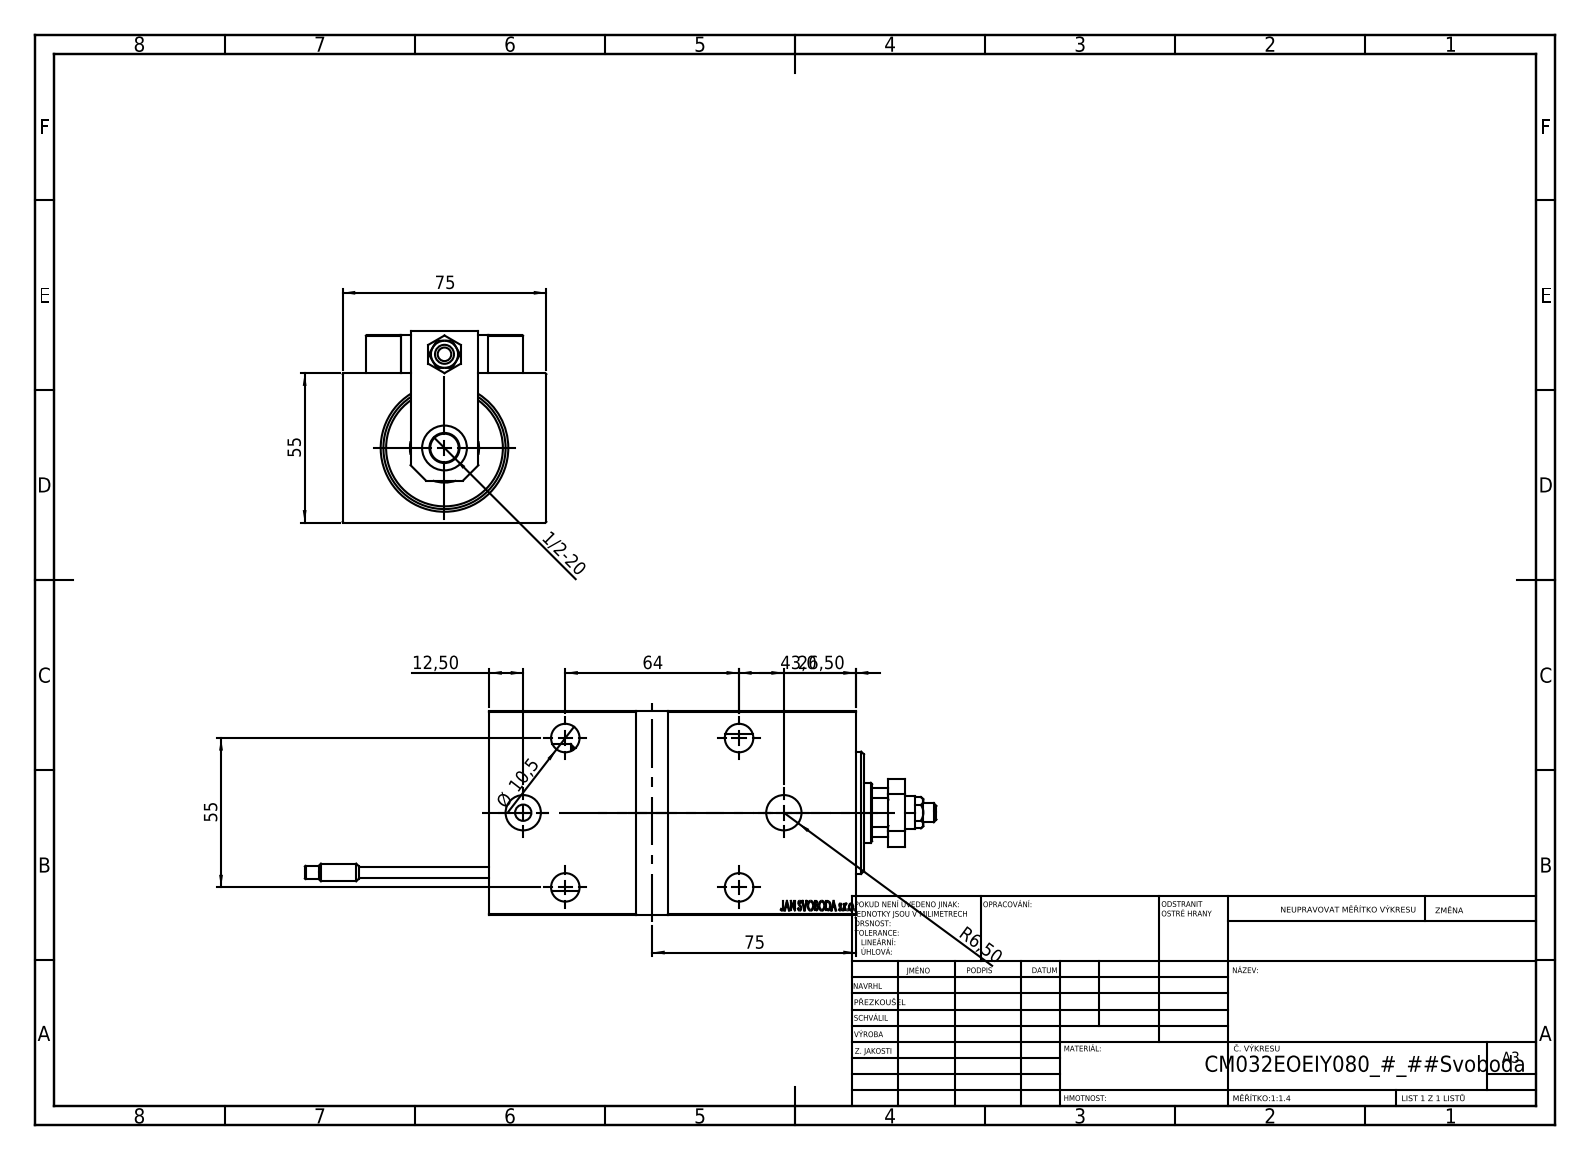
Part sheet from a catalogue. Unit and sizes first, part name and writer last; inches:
Units: inches
Overall size (bounding box): 9.161 × 2.953 × 2.776
Round holes (diameter × count): ⌀0.315 ×5, ⌀0.413 ×5, ⌀0.65 ×5, ⌀0.126 ×4, ⌀0.157 ×4, ⌀0.197 ×2, ⌀0.512 ×2, ⌀0.276 ×1, ⌀0.866 ×1, ⌀1.004 ×1, ⌀1.26 ×1, ⌀1.772 ×1
Round bosses / shafts (diameter × count): ⌀0.197 ×4, ⌀0.256 ×2, ⌀0.15 ×2, ⌀1.339 ×1, ⌀0.512 ×1, ⌀0.433 ×1, ⌀0.236 ×1
Partial cylindrical surfaces — rounded edges, fillets, slot ends (radius × count): R0.012 ×30, R0.118 ×2, R0.413 ×1
Main face-to-face distances: 2.165, 2.953, 0.394, 2.717, 0.551, 0.118, 5.315, 0.472, 0.984, 4.921
Hole centre spacings: 0.448, 0.492, 0.787, 0.863, 1.138, 1.165, 1.169, 1.243
Volume: 33.78 in³ · Surface area: 170.1 in²
Bodies: 24 solids, 1305 faces (570 planar, 182 cylindrical, 553 other)
Part name (STEP PRODUCT): NUT_D12; ZARAZKA; V450CM_E_VCP; KONCOVKA_Y (+7 more)
STEP written by: SolidWorks 2019 (CONFIG_CONTROL_DESIGN)
